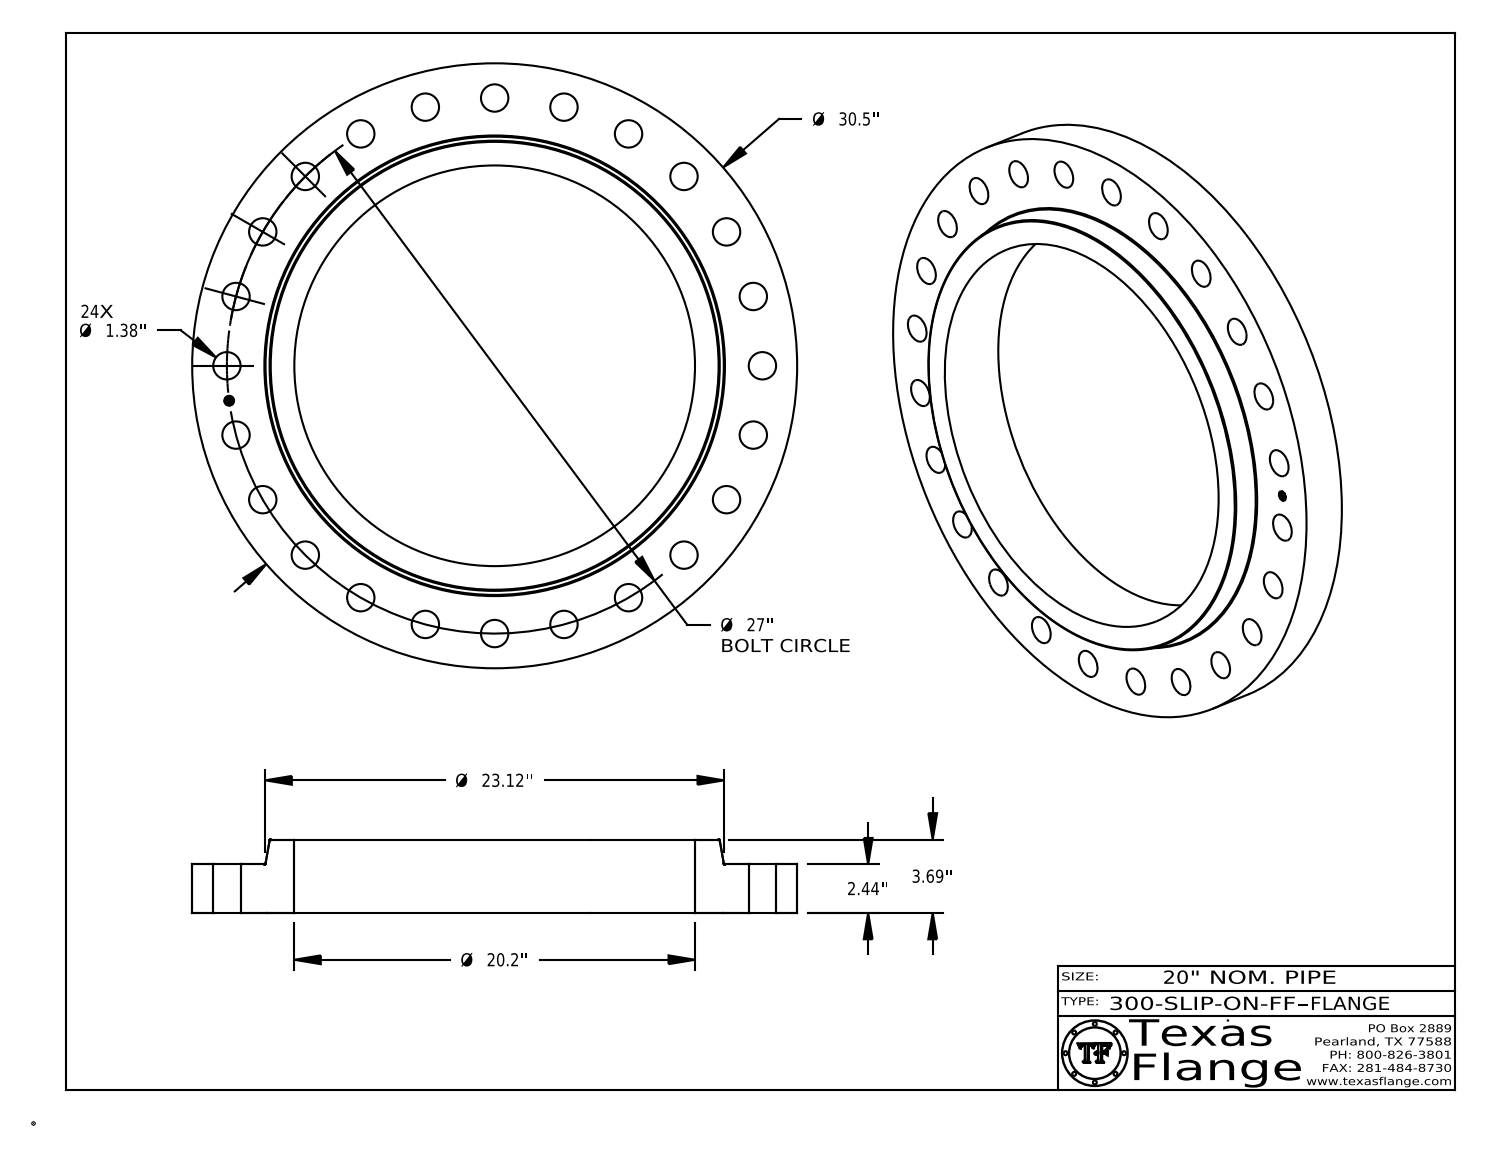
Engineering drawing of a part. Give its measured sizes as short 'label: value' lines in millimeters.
name: 300-SLIP-ON-FF
written by: CATIA V5 STEP AP214 (AUTOMOTIVE_DESIGN)
unit: mm
bodies: 1 solid, 447 faces (369 planar, 72 cylindrical, 6 other)
size: 774.7 × 774.7 × 93.7
volume: 16 830 000 mm³; area: 995 500 mm²
holes: 24× ⌀35.1, 1× ⌀12.6, 1× ⌀513.1
bosses: 8× ⌀0.8, 1× ⌀774.7, 1× ⌀9.9
face distances: 62, 93.7, 31.8, 61.6, 0.4, 32.1, 3.8, 3.7, 0.7, 2.4
hole spacings: 342.9, 89.5, 177.5, 262.5, 417.5, 633.6, 679.9, 544.1
